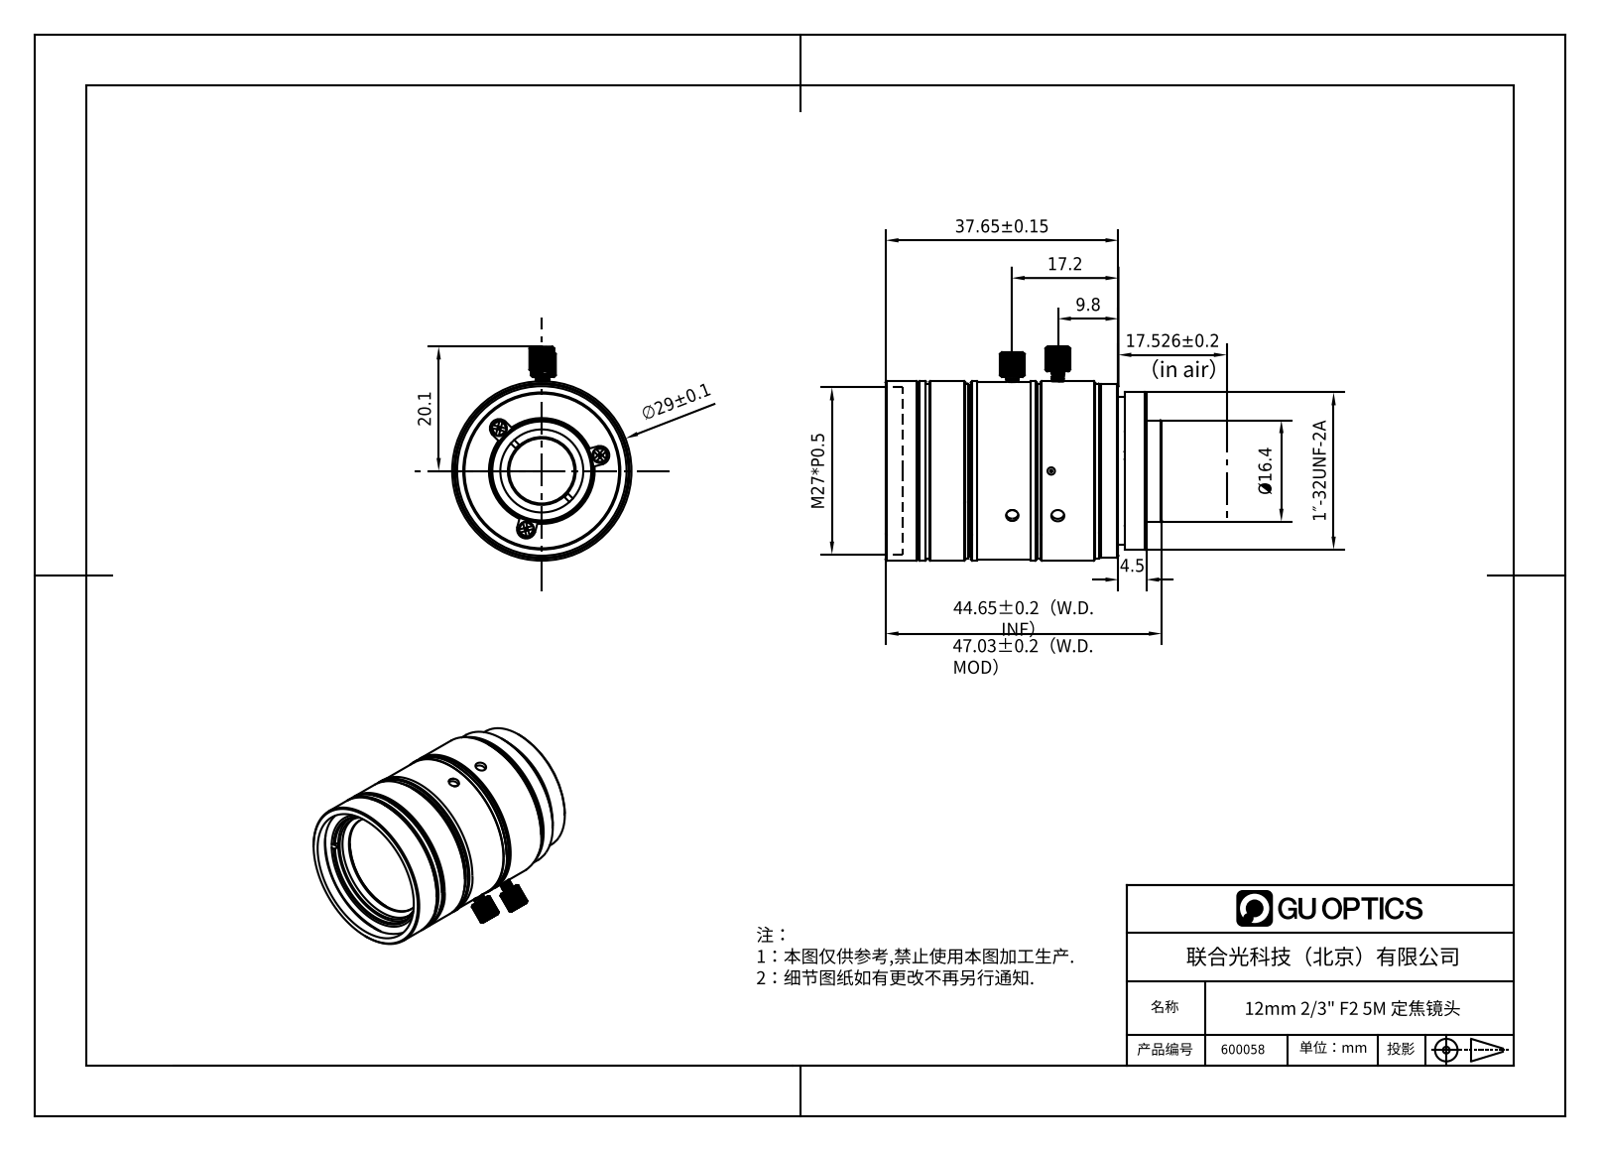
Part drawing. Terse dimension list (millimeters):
name: 600058
written by: SolidWorks 2020 (CONFIG_CONTROL_DESIGN)
unit: mm
bodies: 8 solids, 791 faces (254 planar, 364 cylindrical, 173 other)
size: 44.65 × 29.93 × 29.9
volume: 24 796 mm³; area: 8 469 mm²
holes: 3× ⌀1.1, 3× ⌀1.65, 3× ⌀1.7, 3× ⌀2, 3× ⌀2.1, 1× ⌀10.53, 1× ⌀10.98, 1× ⌀11.2, 1× ⌀13.42, 1× ⌀14.1, 1× ⌀16.7, 1× ⌀19.88
bosses: 6× ⌀1.6, 3× ⌀2.5, 3× ⌀1.2, 2× ⌀2, 1× ⌀29, 1× ⌀28.8, 1× ⌀28.2, 1× ⌀28
rounds: 6× R1.11, 6× R3.39, 6× R3.43, 3× R1.5, 2× R1.12, 2× R2
face distances: 36.51, 2.5, 42.15, 39.65, 0.44, 36.13, 3.52, 4.5, 31.63, 35.15
hole spacings: 16.88, 9.74, 9.75
